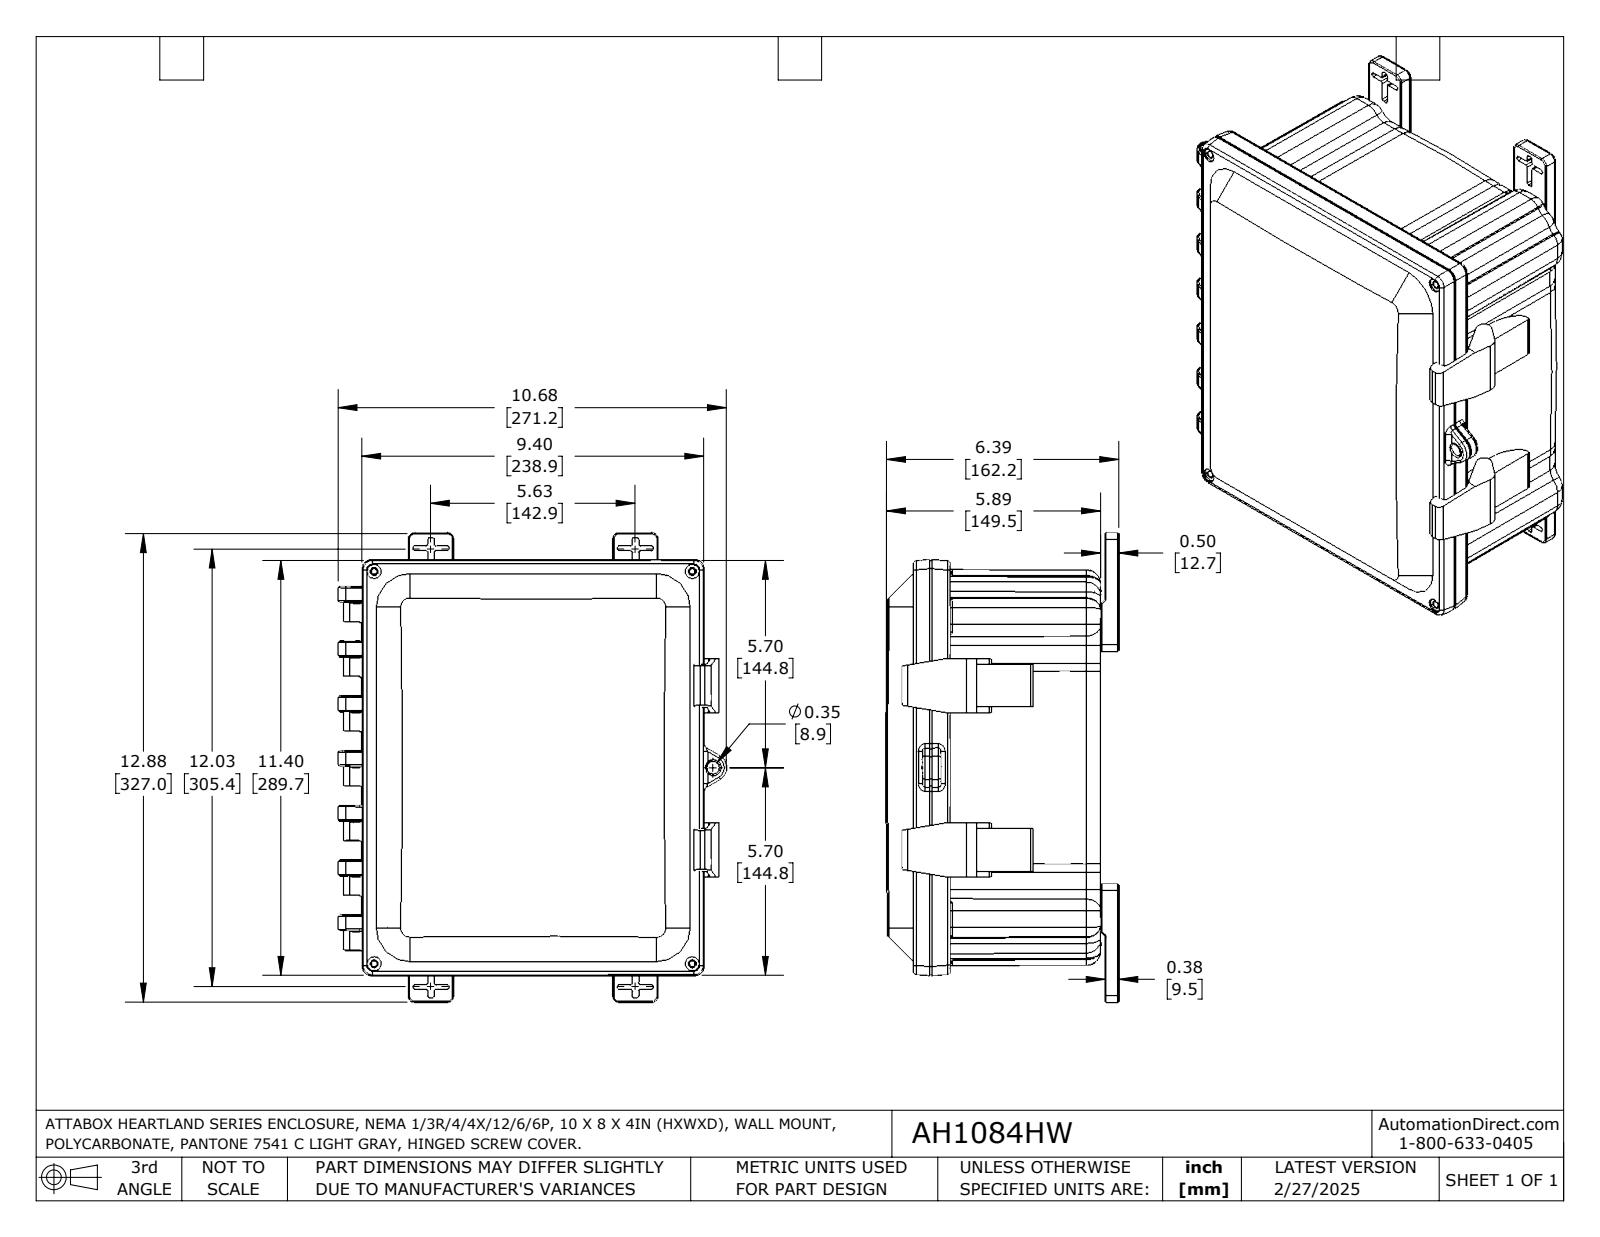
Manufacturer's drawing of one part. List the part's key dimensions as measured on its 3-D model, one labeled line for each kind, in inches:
Part name (STEP PRODUCT): AH1084HW_REV1
STEP written by: SolidWorks 2024 (AUTOMOTIVE_DESIGN)
Units: inches
Bodies: 6 solids, 2421 faces (632 planar, 798 cylindrical, 991 other)
Overall size (bounding box): 12.875 × 10.676 × 6.388
Volume: 88.92 in³ · Surface area: 961.5 in²
Round holes (diameter × count): ⌀0.156 ×8, ⌀0.195 ×4, ⌀0.25 ×4, ⌀0.313 ×4, ⌀0.39 ×4, ⌀0.327 ×1, ⌀0.375 ×1, ⌀0.45 ×1
Round bosses / shafts (diameter × count): ⌀0.25 ×4, ⌀0.313 ×1
Partial cylindrical surfaces — rounded edges, fillets, slot ends (radius × count): R0.05 ×116, R0.035 ×104, R0.065 ×81, R0.03 ×52, R0.02 ×32, R0.025 ×26, R0.01 ×25, R0.18 ×16
Main face-to-face distances: 0.14, 4.64, 4.5, 0.5, 5.14, 0.133, 4.14, 4, 0.43, 0.64
Hole centre spacings: 7.604, 8.75, 7.355, 11.665, 12.104, 0.442, 1.768, 2.21
